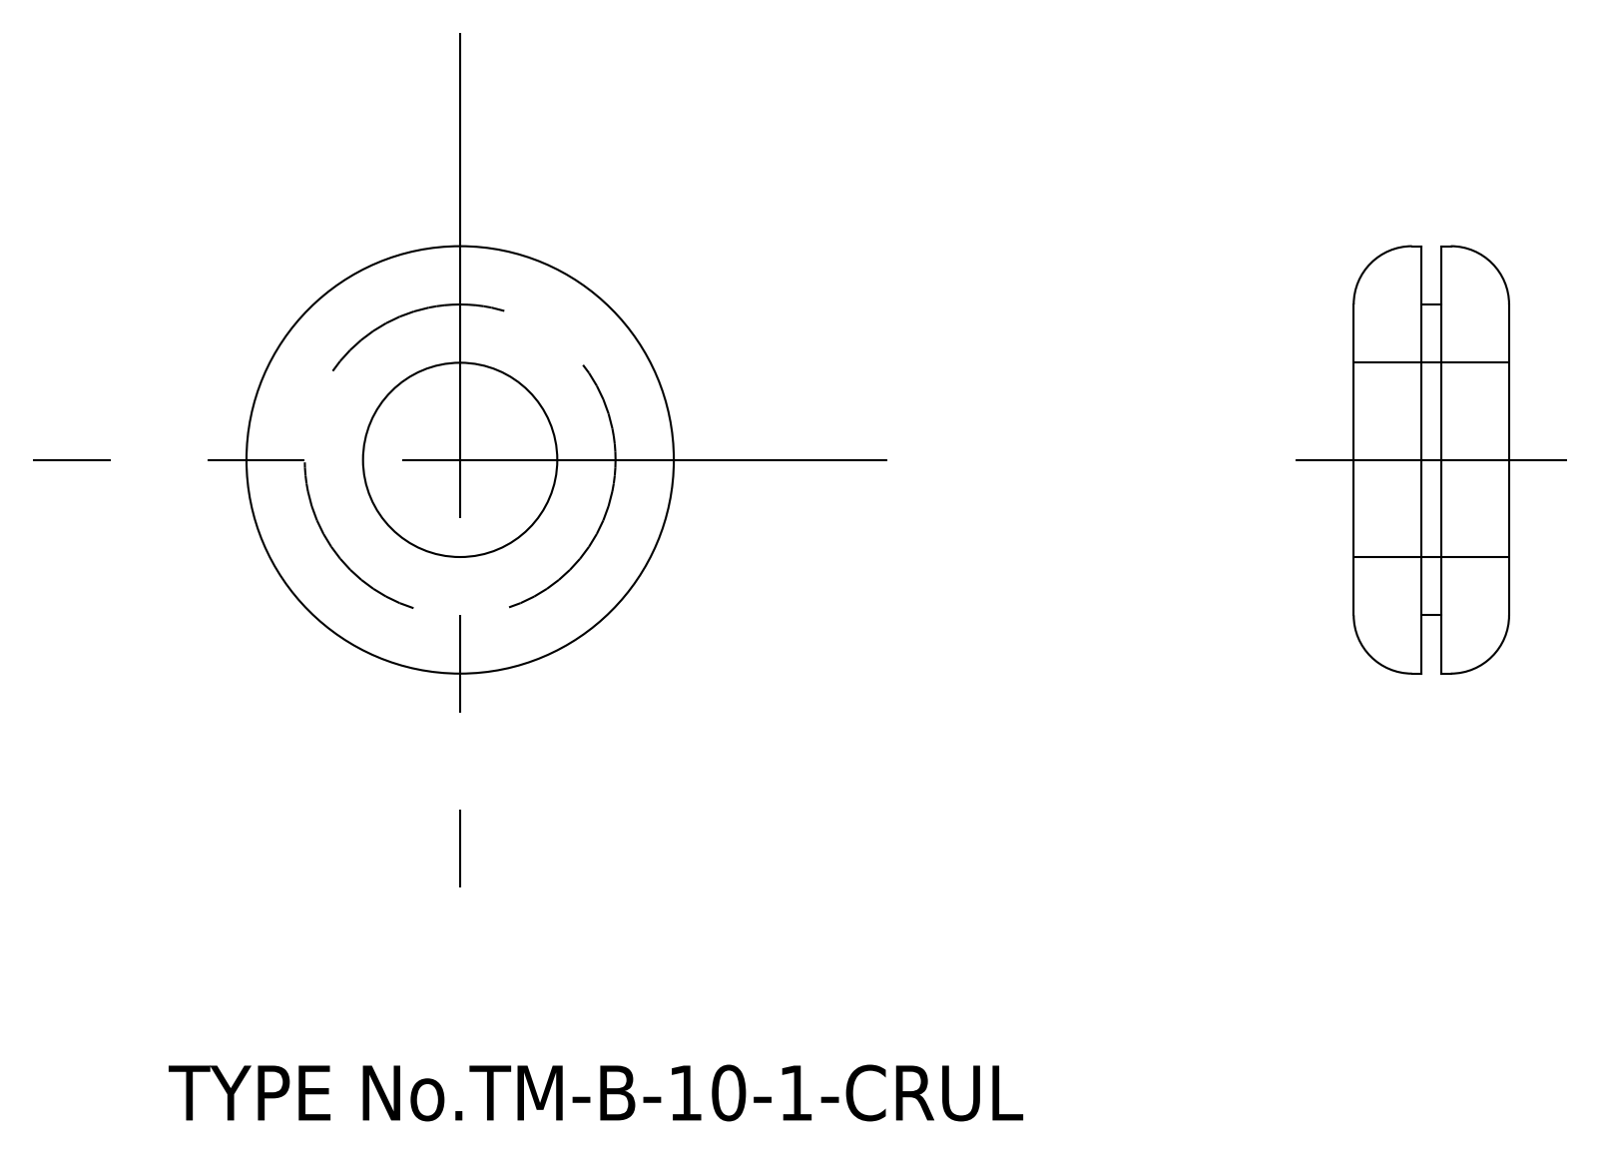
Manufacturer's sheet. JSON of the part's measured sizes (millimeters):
{"step_written_by": "spGate 15.6.1 (AUTOMOTIVE_DESIGN)", "units": "millimeters", "bodies": {"solids": 1, "faces": 16, "planar": 4, "cylindrical": 8, "other": 4}, "overall_size": [22, 22, 8], "volume_mm3": 1984, "surface_area_mm2": 1561, "round_holes": [[10, 1]], "round_bosses_or_shafts": [[22, 1], [16, 1]], "face_to_face_distances": [3.5, 4.5, 1, 8]}
